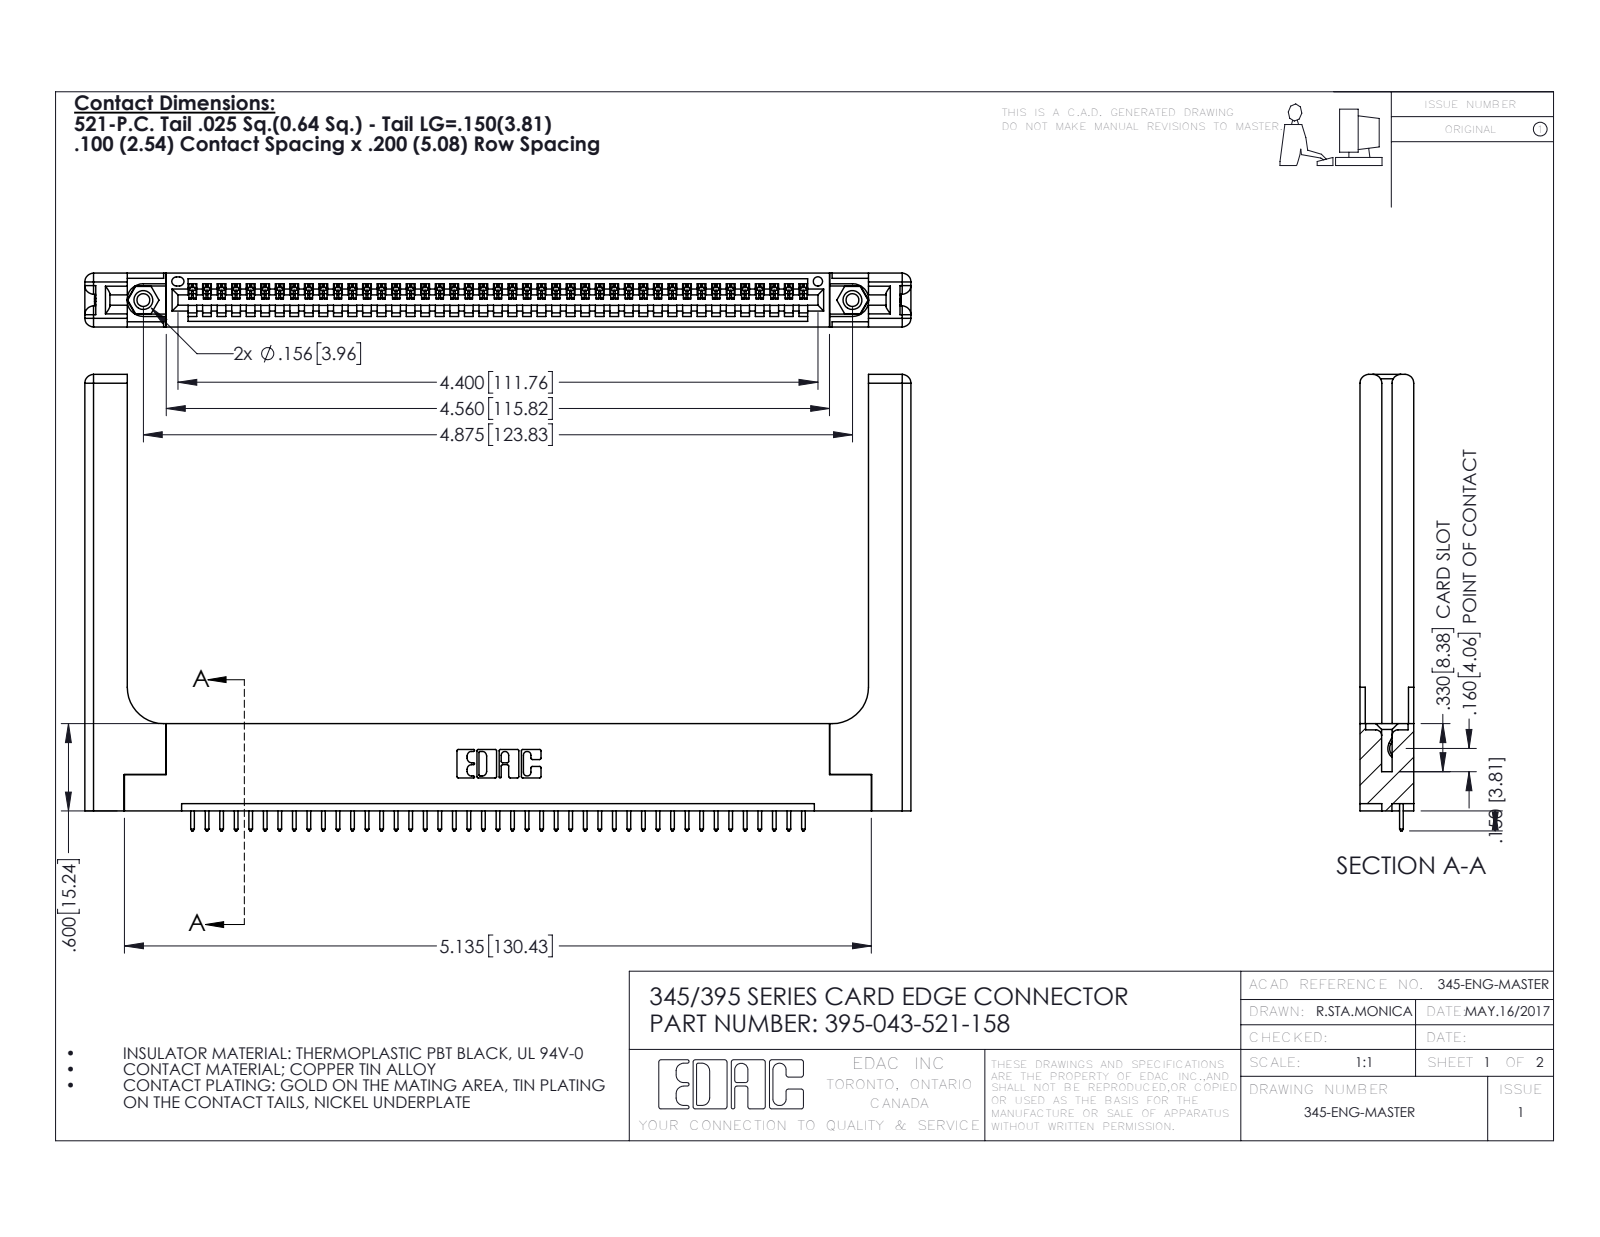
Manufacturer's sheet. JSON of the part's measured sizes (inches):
{"part_name": "345-250-001_345-250-001-102; 395-043-521-158; 345-220-058_345-220-058; 345-292-001_345-293-121 (+1 more)", "step_written_by": "SolidWorks 2016 (CONFIG_CONTROL_DESIGN)", "units": "inches", "bodies": {"solids": 48, "faces": 2876, "planar": 1948, "cylindrical": 868, "other": 60}, "overall_size": [5.679, 3.137, 0.37], "volume_in3": 1.348, "surface_area_in2": 35.49, "round_holes": [[0.089, 2], [0.125, 2], [0.156, 2], [0.064, 1]], "round_bosses_or_shafts": [[0.155, 2]], "partial_cylinders_radius": [[0.006, 86], [0.01, 86], [0.01, 22], [0.06, 16], [0.007, 6], [0.031, 6], [0.026, 3], [0.03, 2]], "face_to_face_distances": [0.37, 0.072, 0.298, 0.2, 0.098, 0.272, 0.025, 0.225, 0.148, 0.15], "hole_center_spacings": [0.27, 4.639, 4.875]}
